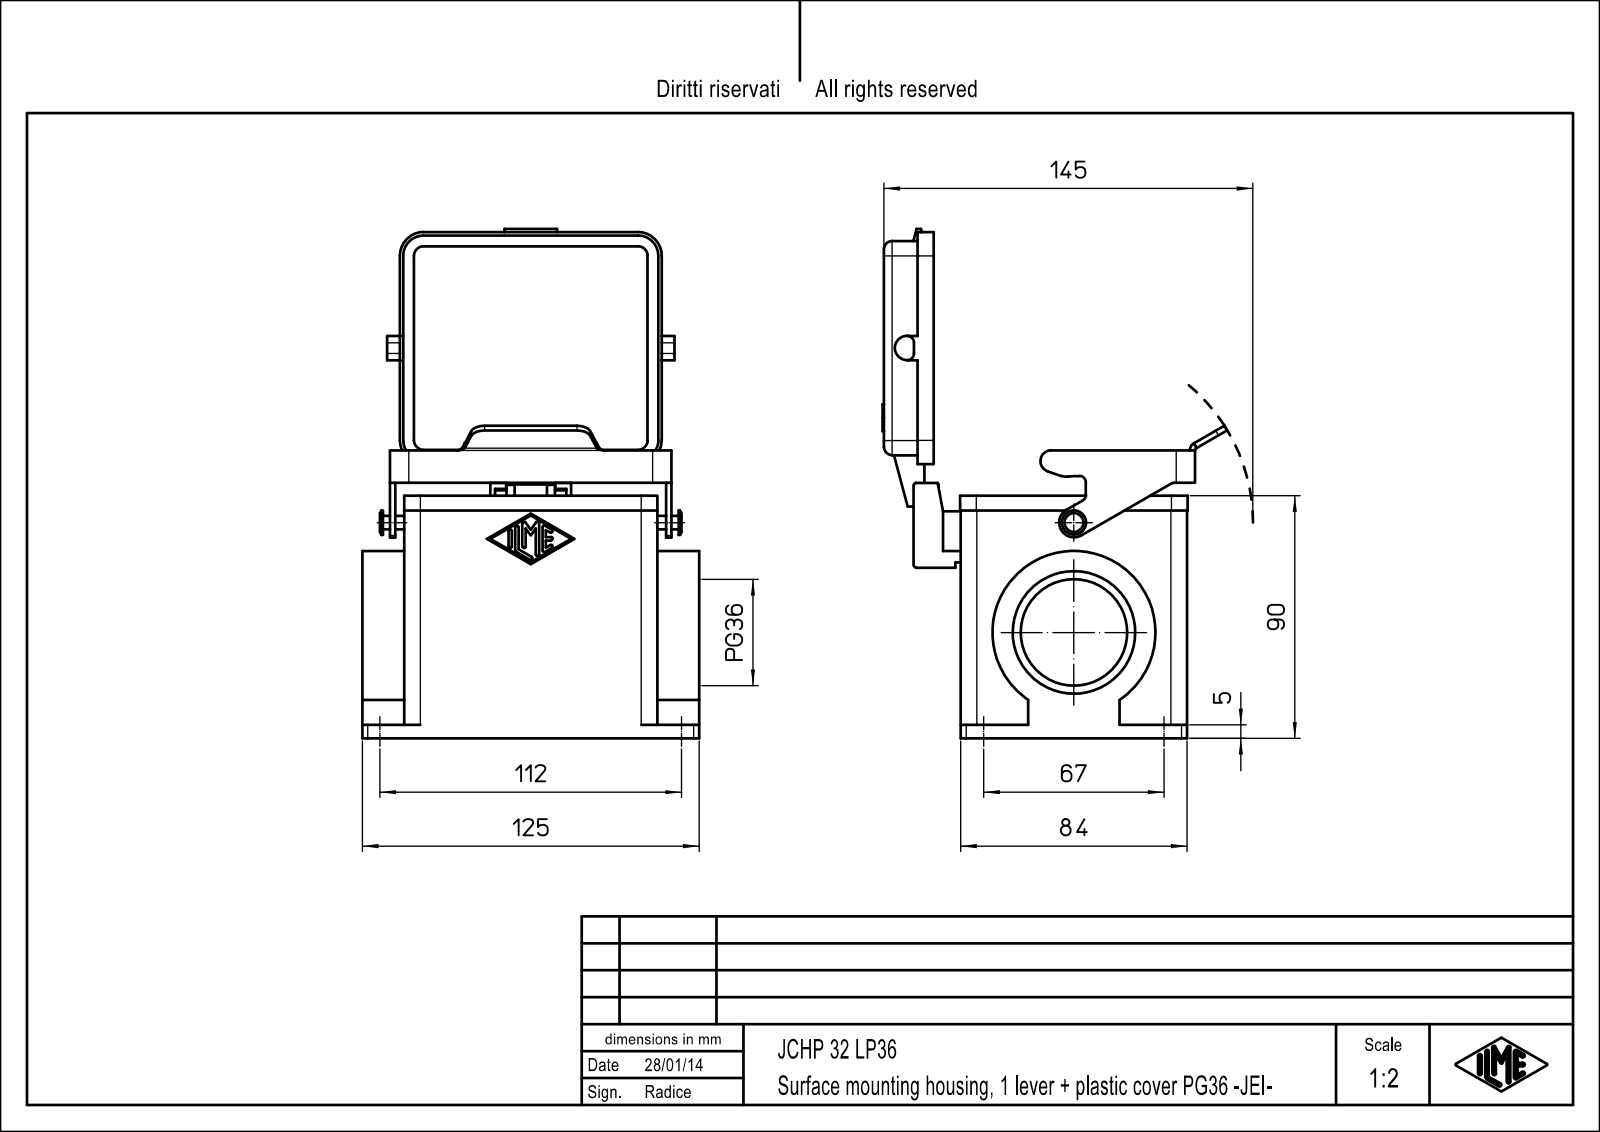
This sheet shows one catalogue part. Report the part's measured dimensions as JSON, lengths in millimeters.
{"part_name": "JCHP_32_LP36", "step_written_by": "Creo Elements/Direct Modeling 18.0B 02-Dec-2011 (C) Parametric Technology GmbH (AUTOMOTIVE_DESIGN)", "units": "millimeters", "bodies": {"solids": 1, "faces": 492, "planar": 281, "cylindrical": 188, "other": 23}, "overall_size": [189, 137.35, 125], "volume_mm3": 289199, "surface_area_mm2": 132994, "round_holes": [[2.46, 8], [3, 8], [5.5, 4], [4, 1], [39.48, 1], [45.48, 1]], "round_bosses_or_shafts": [[60.5, 1], [9, 1], [7, 1], [5, 1], [4, 1]], "partial_cylinders_radius": [[0.62, 14], [3, 11], [1.5, 9], [2, 8], [6, 8], [0.33, 6], [5, 5], [5.5, 5]], "face_to_face_distances": [3, 109.5, 81, 28.5, 2, 106.5, 4, 11.5, 84, 25.5], "hole_center_spacings": [17.37, 27, 33.74, 36, 41.73, 67.25, 77.5, 82.07]}
